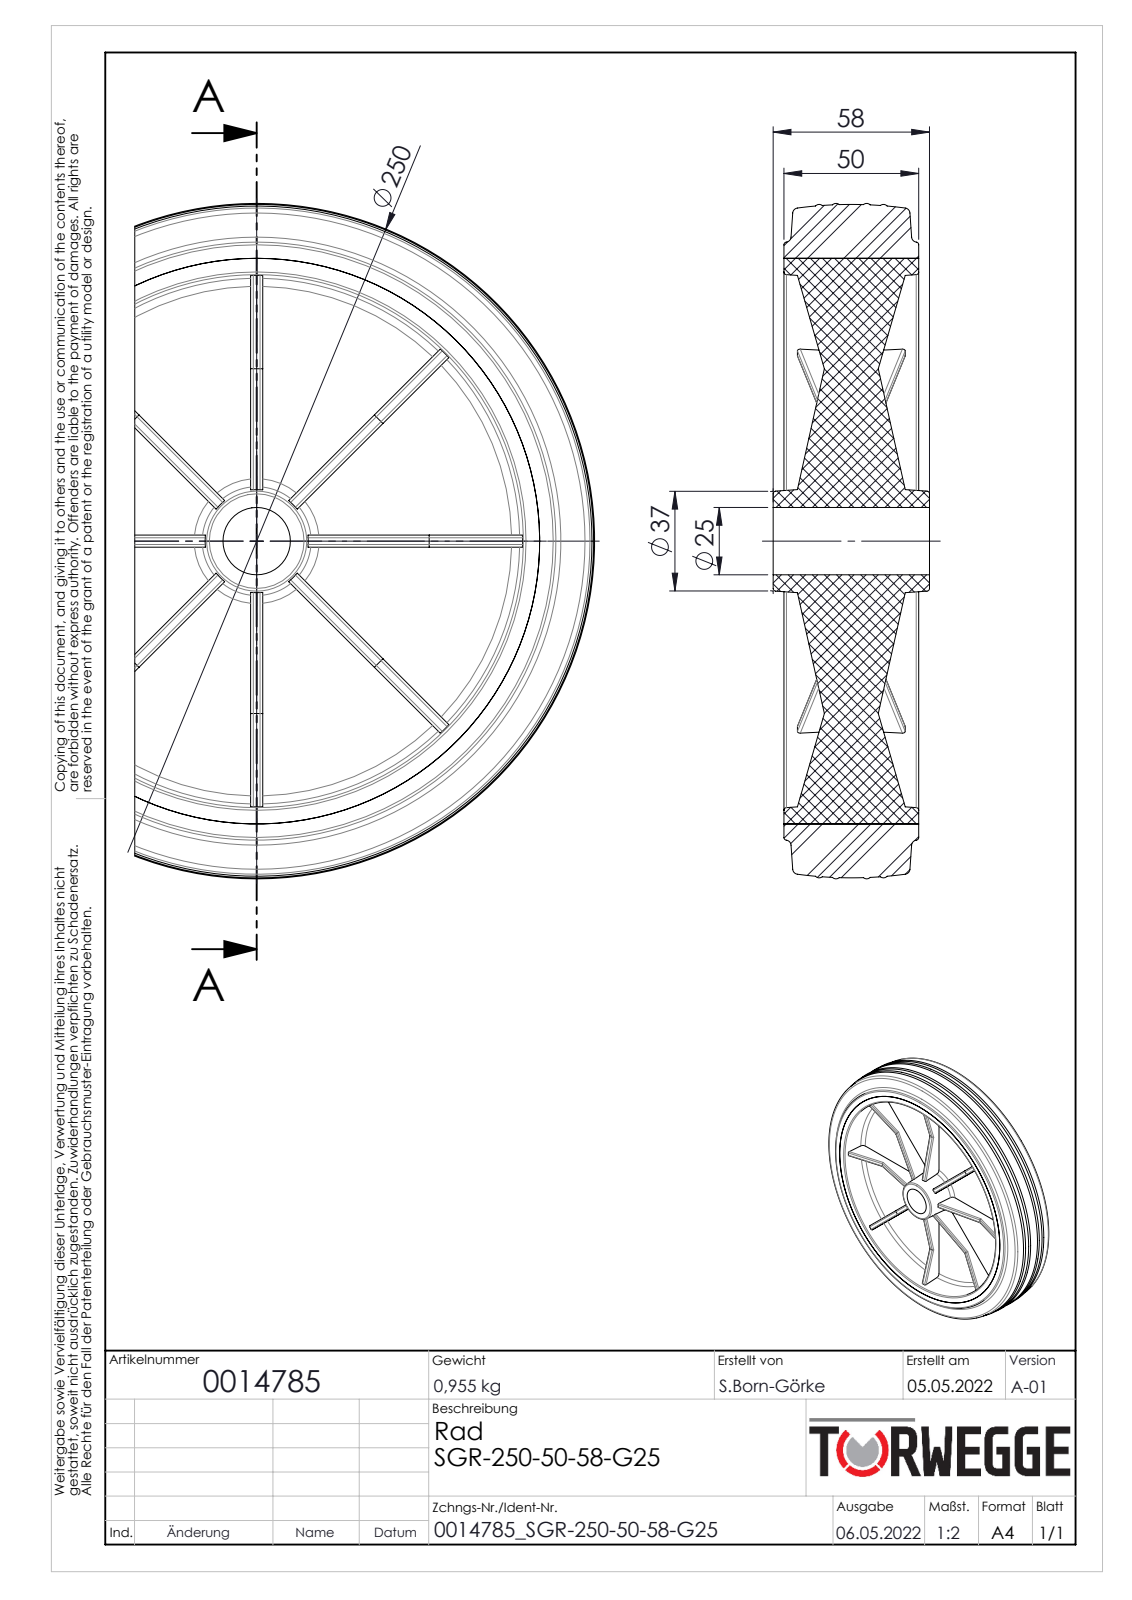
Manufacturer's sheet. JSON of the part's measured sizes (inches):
{"part_name": "0014785", "step_written_by": "SolidWorks 2020 (AUTOMOTIVE_DESIGN)", "units": "inches", "bodies": {"solids": 2, "faces": 246, "planar": 86, "cylindrical": 70, "other": 90}, "overall_size": [9.873, 9.873, 2.283], "volume_in3": 66.76, "surface_area_in2": 404.2, "round_holes": [[0.984, 1], [8.268, 1]], "partial_cylinders_radius": [[0.039, 64]], "face_to_face_distances": [0.157, 0.177, 1.063, 0.906, 1.969, 1.22, 2.126, 2.283, 1.866, 1.866]}
